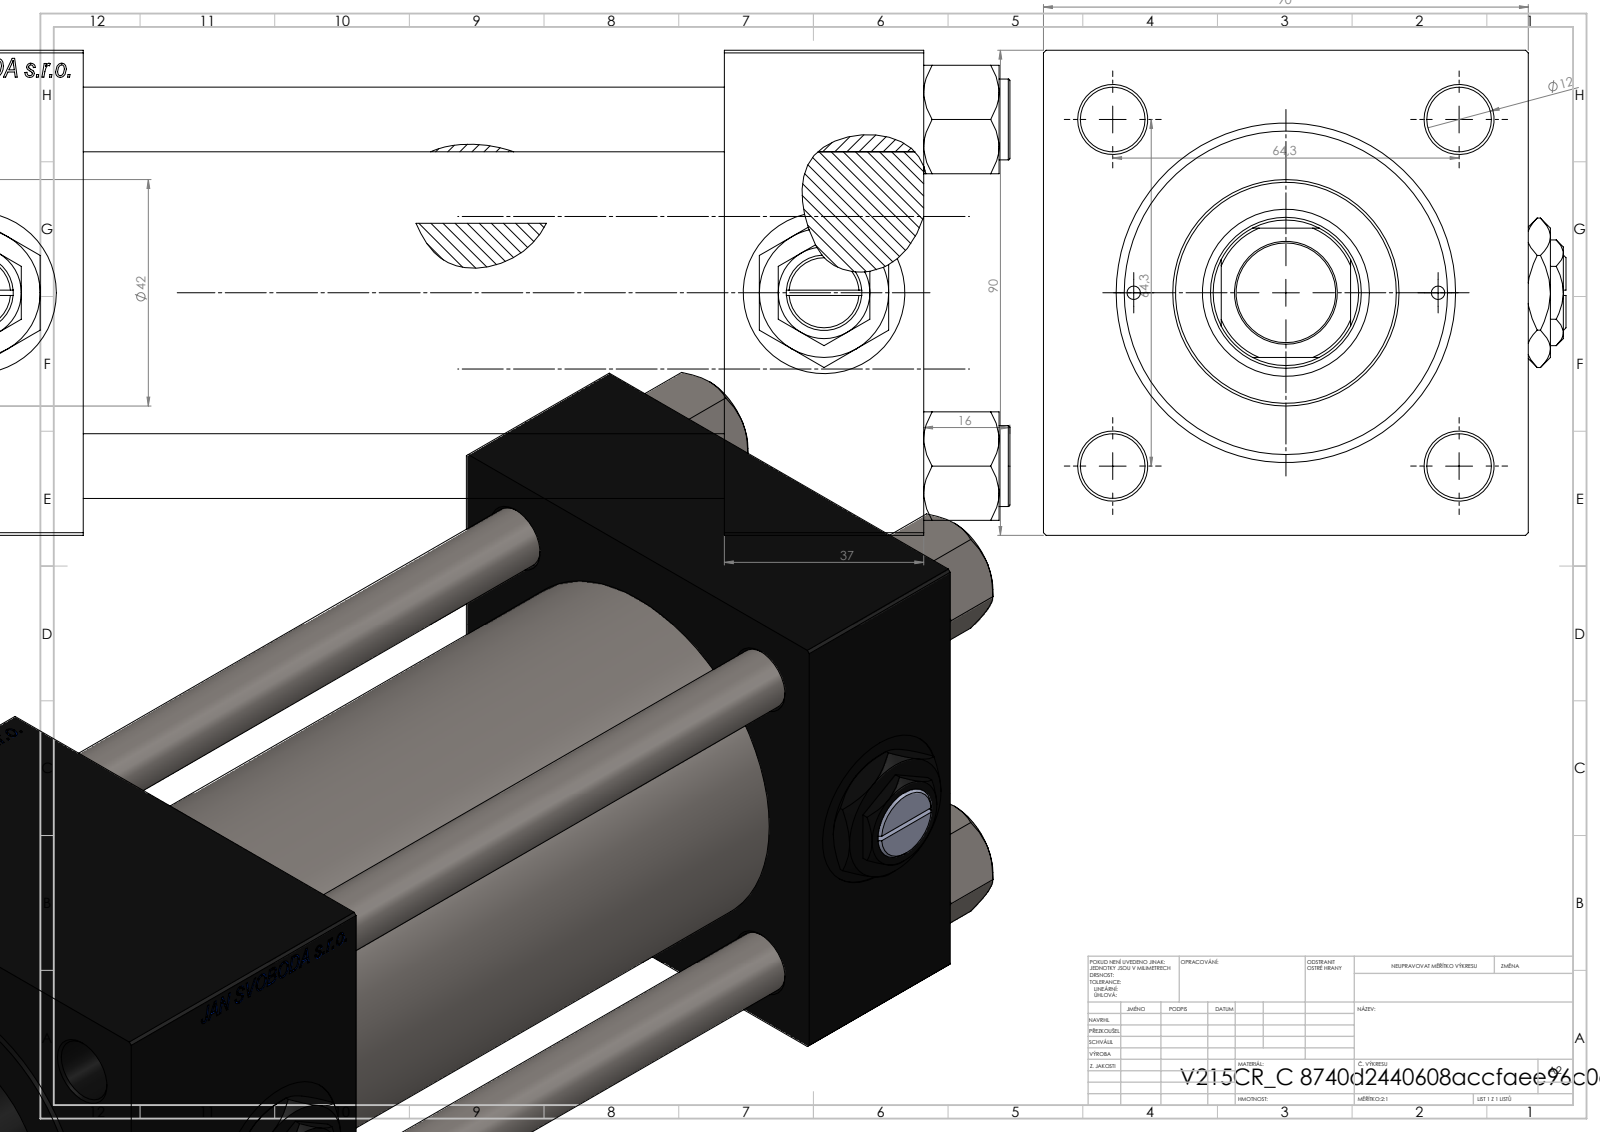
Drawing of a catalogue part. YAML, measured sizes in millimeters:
part_name: "Zatka_pro_OIL_PORT; V215_VC_A; V215CR_C_Body; NUT_M5_C (+2 more)"
step_written_by: "SolidWorks 2019 (CONFIG_CONTROL_DESIGN)"
units: millimeters
bodies: {solids: 13, faces: 1256, planar: 576, cylindrical: 102, other: 578}
overall_size: [263, 97, 90]
volume: 1042000
surface_area: 223201
round_holes:
  - {diameter: 12, count: 4}
  - {diameter: 2.5, count: 2}
  - {diameter: 7, count: 2}
  - {diameter: 20.96, count: 2}
  - {diameter: 30, count: 2}
  - {diameter: 18.5, count: 1}
  - {diameter: 28, count: 1}
  - {diameter: 31, count: 1}
  - {diameter: 50, count: 1}
  - {diameter: 60, count: 1}
  - {diameter: 63, count: 1}
round_bosses_or_shafts:
  - {diameter: 15, count: 4}
  - {diameter: 69, count: 1}
  - {diameter: 42, count: 1}
partial_cylinders:
  - {radius: 13.5, count: 1}
face_to_face_distances: [90, 37, 178, 215, 59, 156, 119, 186.3, 149.3, 30.3]
hole_center_spacings: [32.39, 45.47, 64.3, 68.42, 28.25, 90.93, 56.5, 157.5]
